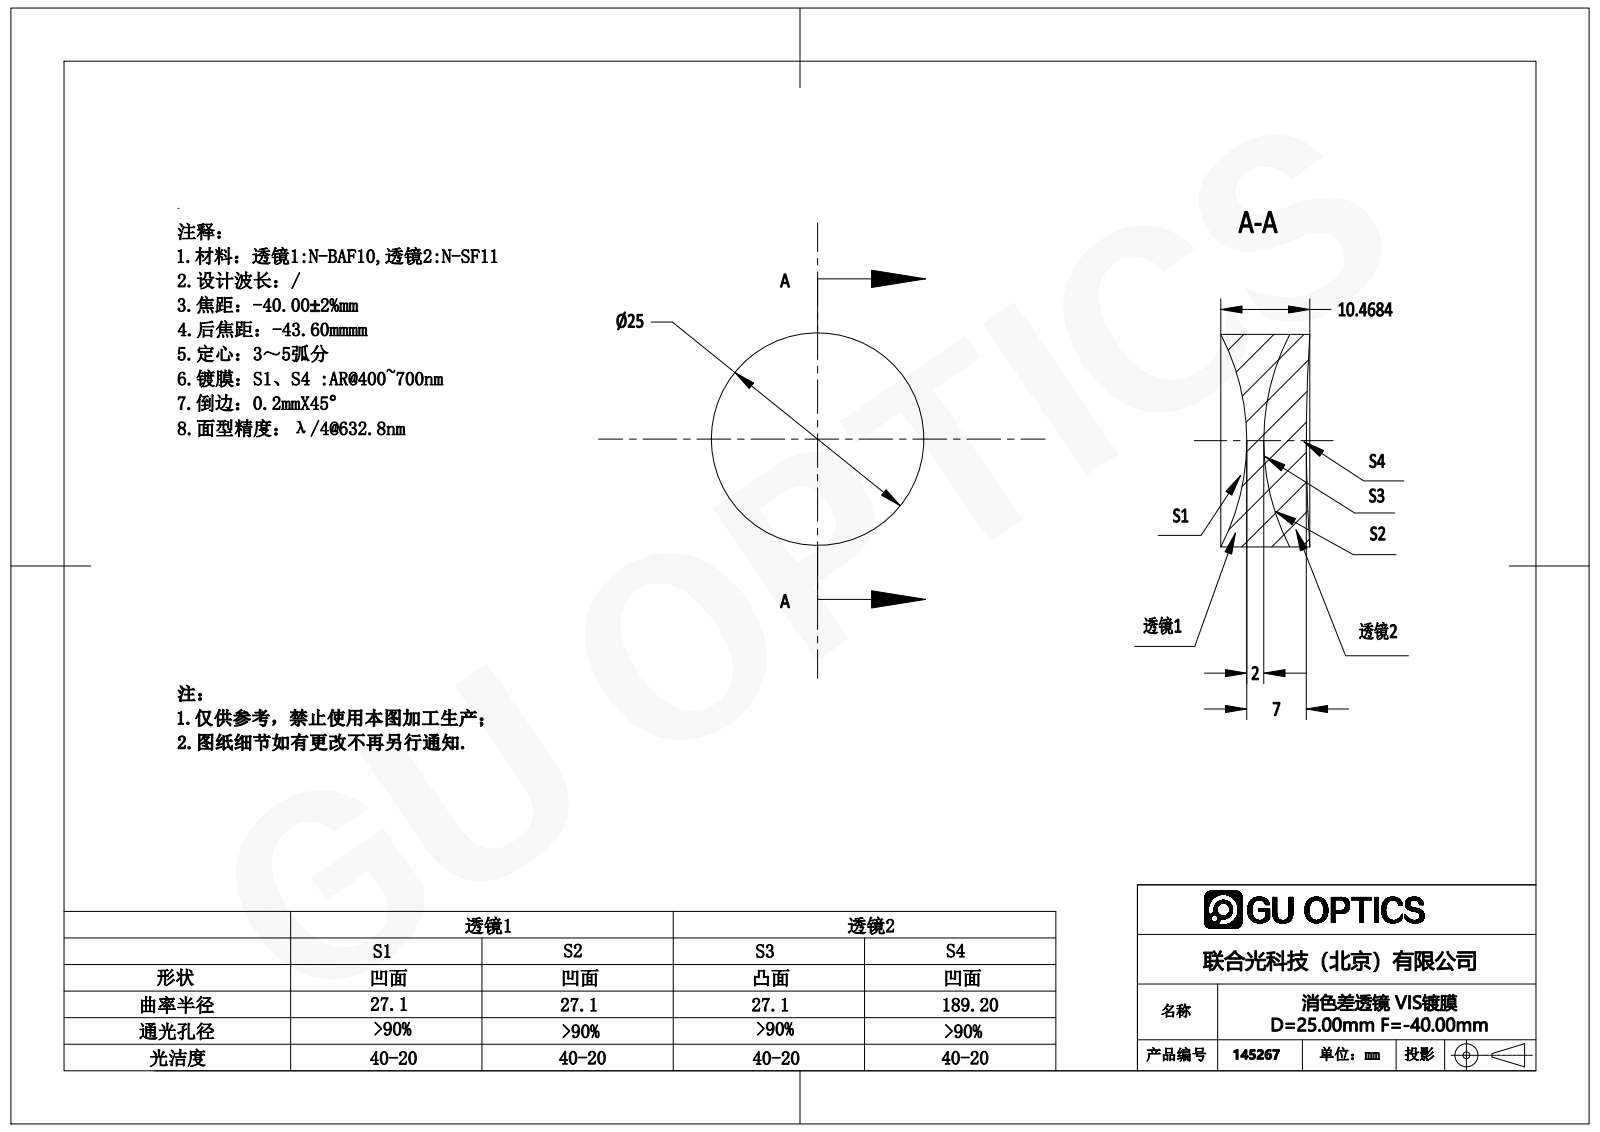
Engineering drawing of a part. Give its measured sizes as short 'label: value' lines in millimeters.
name: 145267
written by: SolidWorks 2020 (CONFIG_CONTROL_DESIGN)
unit: mm
bodies: 2 solids, 8 faces (0 planar, 0 cylindrical, 8 other)
size: 25 × 25 × 10.47
volume: 4 274 mm³; area: 2 875 mm²
